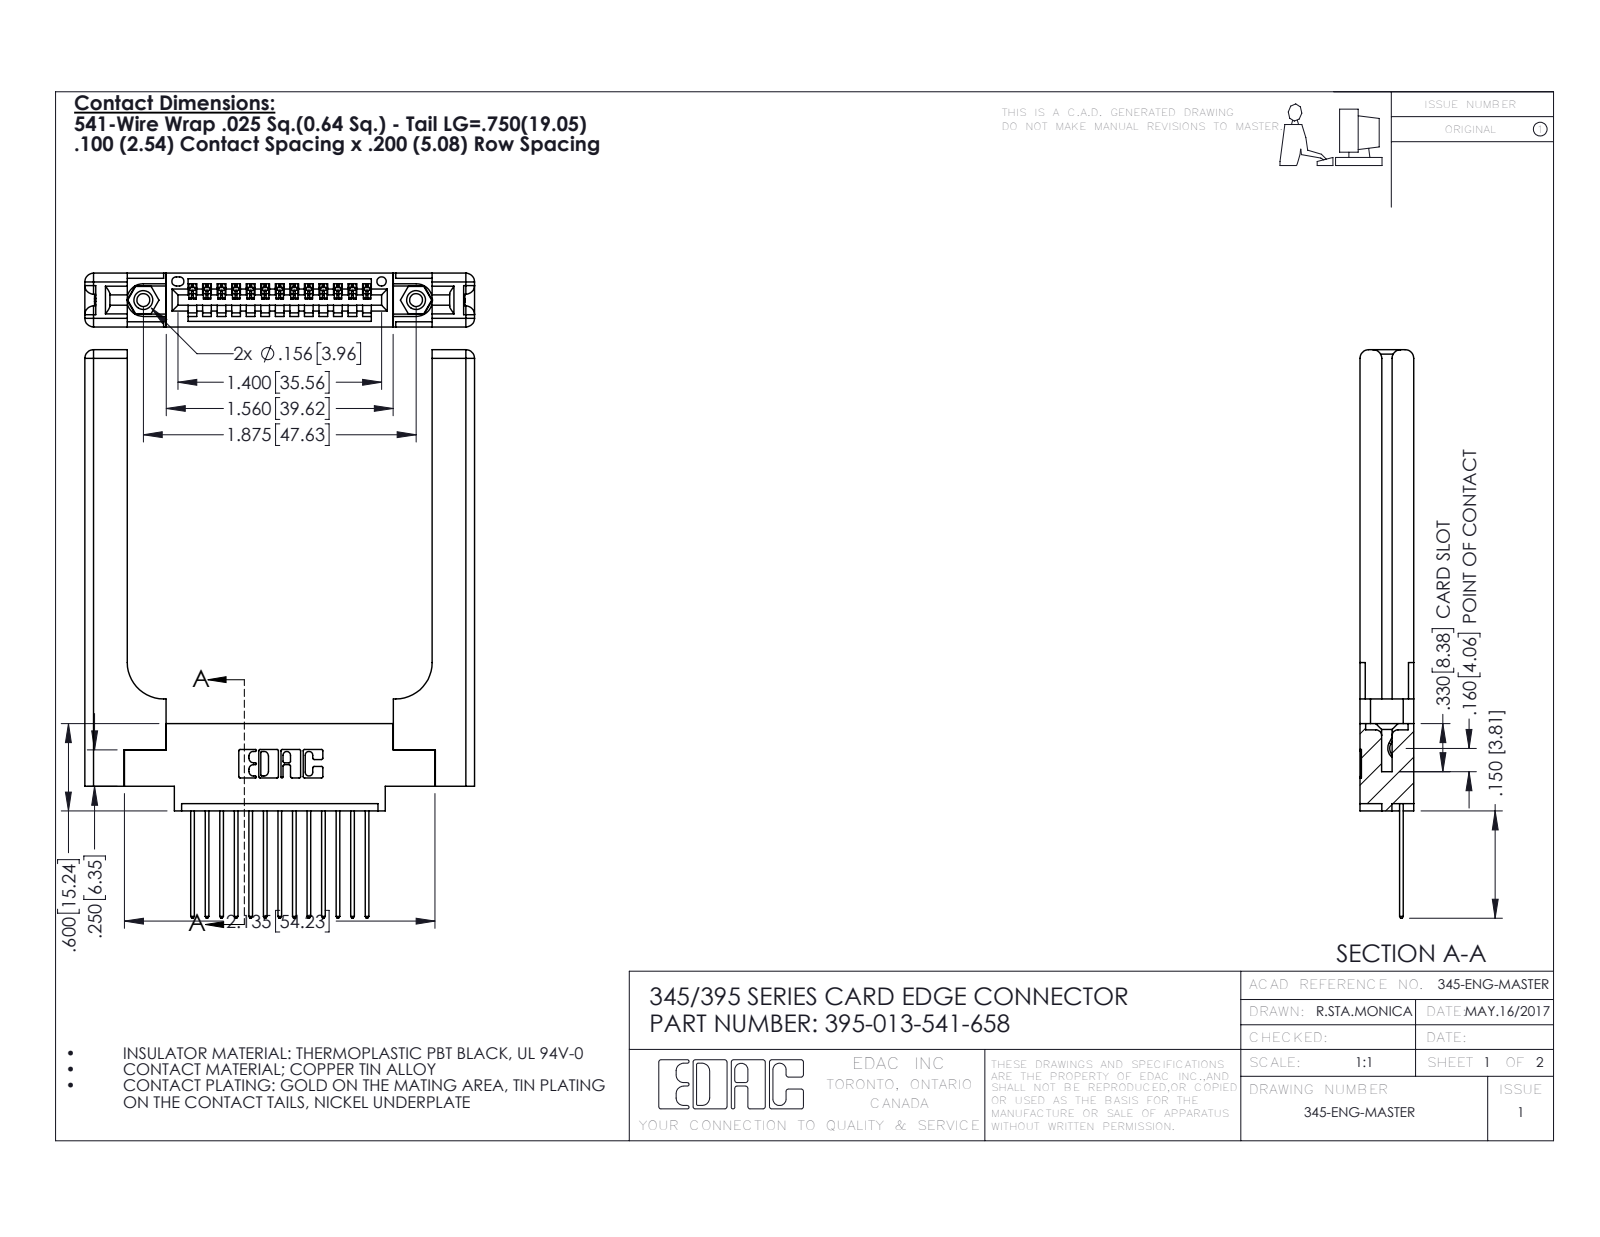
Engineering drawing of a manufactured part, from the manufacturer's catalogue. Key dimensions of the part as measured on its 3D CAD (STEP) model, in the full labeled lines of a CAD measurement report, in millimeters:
Part name (STEP PRODUCT): 345-292-001_345-293-141; 395-013-541-658; 345 Part_0.170 Offset - 0.156 Dia-TH; 345-250-001_345-250-001-102 (+1 more)
STEP written by: SolidWorks 2016 (CONFIG_CONTROL_DESIGN)
Units: millimetres
Bodies: 18 solids, 1140 faces (752 planar, 328 cylindrical, 60 other)
Overall size (bounding box): 99.2 × 68 × 9.4
Volume: 14 700 mm³ · Surface area: 13 470 mm²
Round holes (diameter × count): ⌀2.3 ×2, ⌀3.2 ×2, ⌀4 ×2, ⌀1.6 ×1
Round bosses / shafts (diameter × count): ⌀3.9 ×2
Partial cylindrical surfaces — rounded edges, fillets, slot ends (radius × count): R0.2 ×26, R0.3 ×26, R0.3 ×22, R1.5 ×16, R0.2 ×6, R0.8 ×6, R0.7 ×3, R0.8 ×2
Main face-to-face distances: 9.4, 1.8, 7.6, 3.8, 3.8, 2, 5.6, 2.5, 6.9, 0.6
Hole centre spacings: 6.9, 41.7, 47.6
